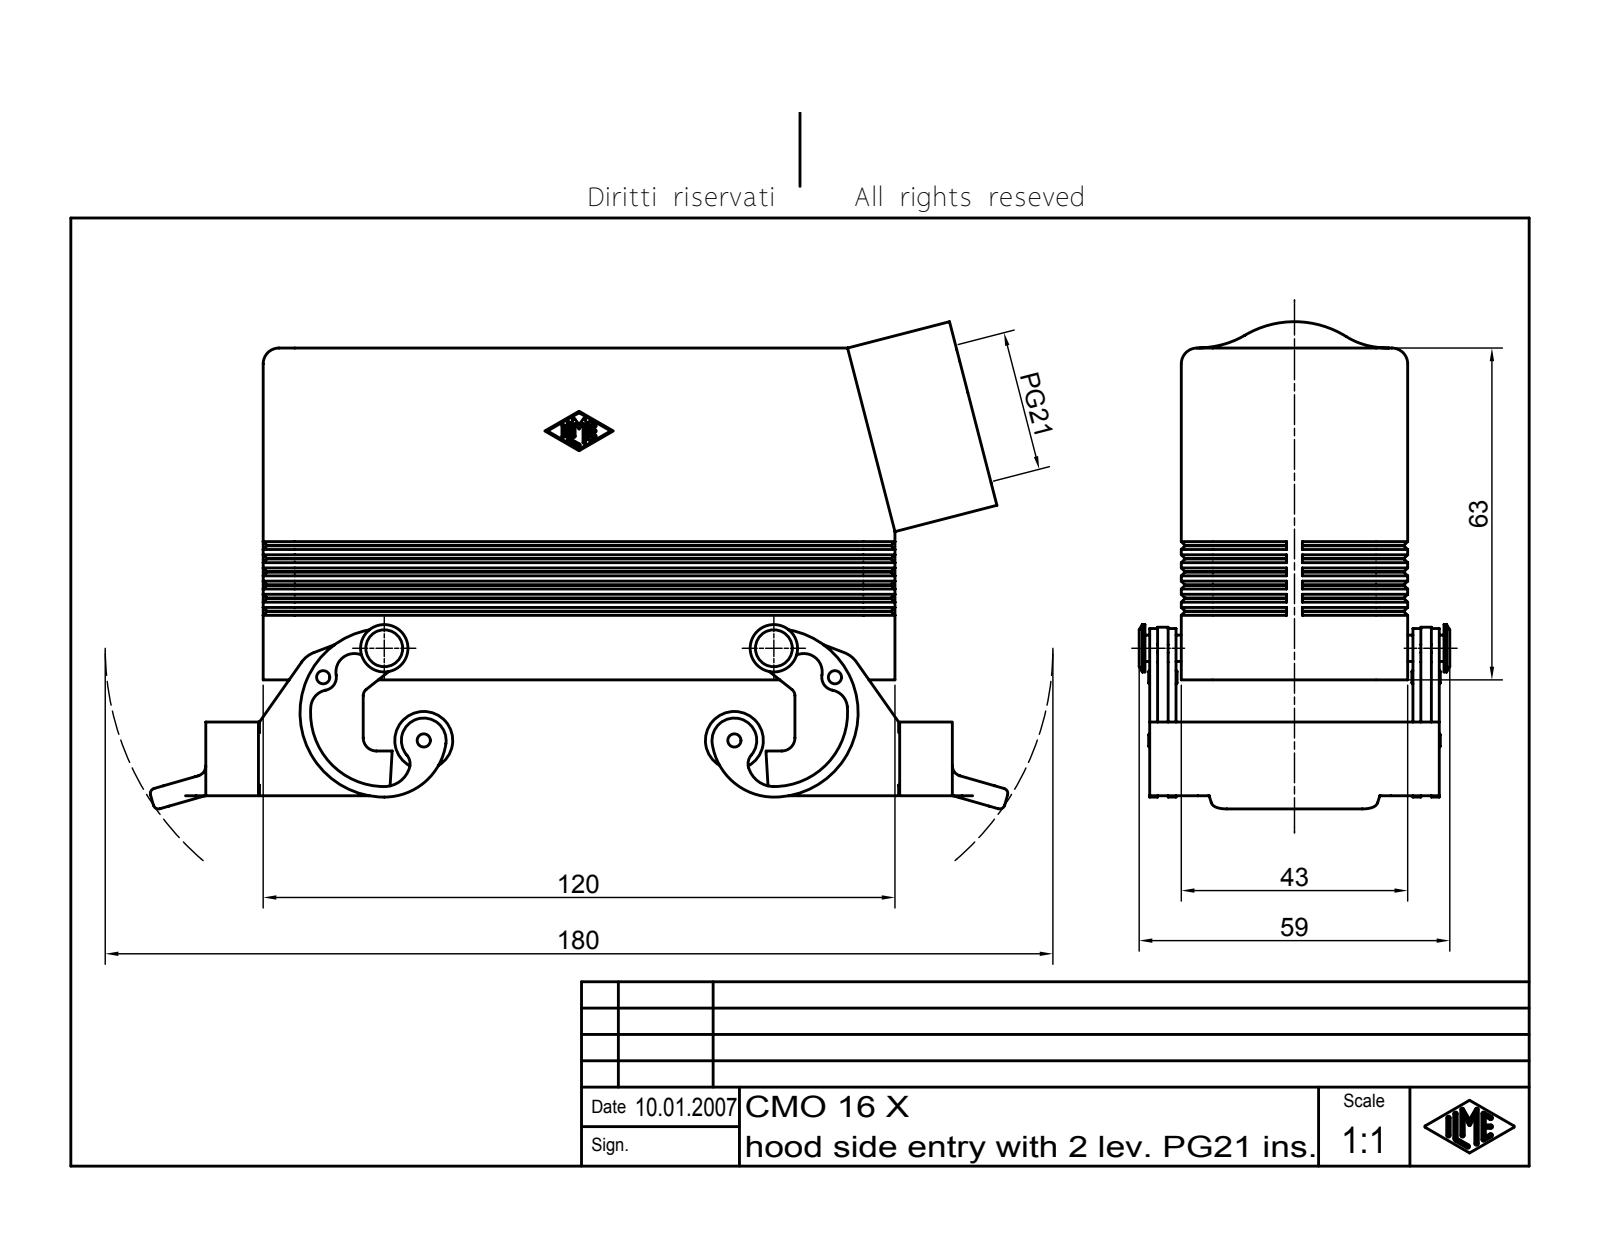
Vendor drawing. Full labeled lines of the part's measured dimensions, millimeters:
Part name (STEP PRODUCT): CHO Tüllengehäuse 2 Bügel für einen Einsatz
STEP written by: Autodesk Inventor 7 (AUTOMOTIVE_DESIGN)
Units: millimetres
Bodies: 1 solid, 927 faces (275 planar, 233 cylindrical, 419 other)
Overall size (bounding box): 162.87 × 92.5 × 59
Volume: 112 762 mm³ · Surface area: 67 865 mm²
Round holes (diameter × count): ⌀2.5 ×2, ⌀24.78 ×1, ⌀26.78 ×1
Round bosses / shafts (diameter × count): ⌀11 ×2, ⌀9 ×2, ⌀5 ×2, ⌀2 ×2
Partial cylindrical surfaces — rounded edges, fillets, slot ends (radius × count): R0.25 ×14, R1 ×12, R3 ×11, R2 ×10, R2.5 ×6, R3.5 ×4, R5 ×4, R6 ×4
Main face-to-face distances: 3, 40, 37, 43, 11.5, 8.5, 1.77, 5.3, 50, 105.5
Hole centre spacings: 97.2
